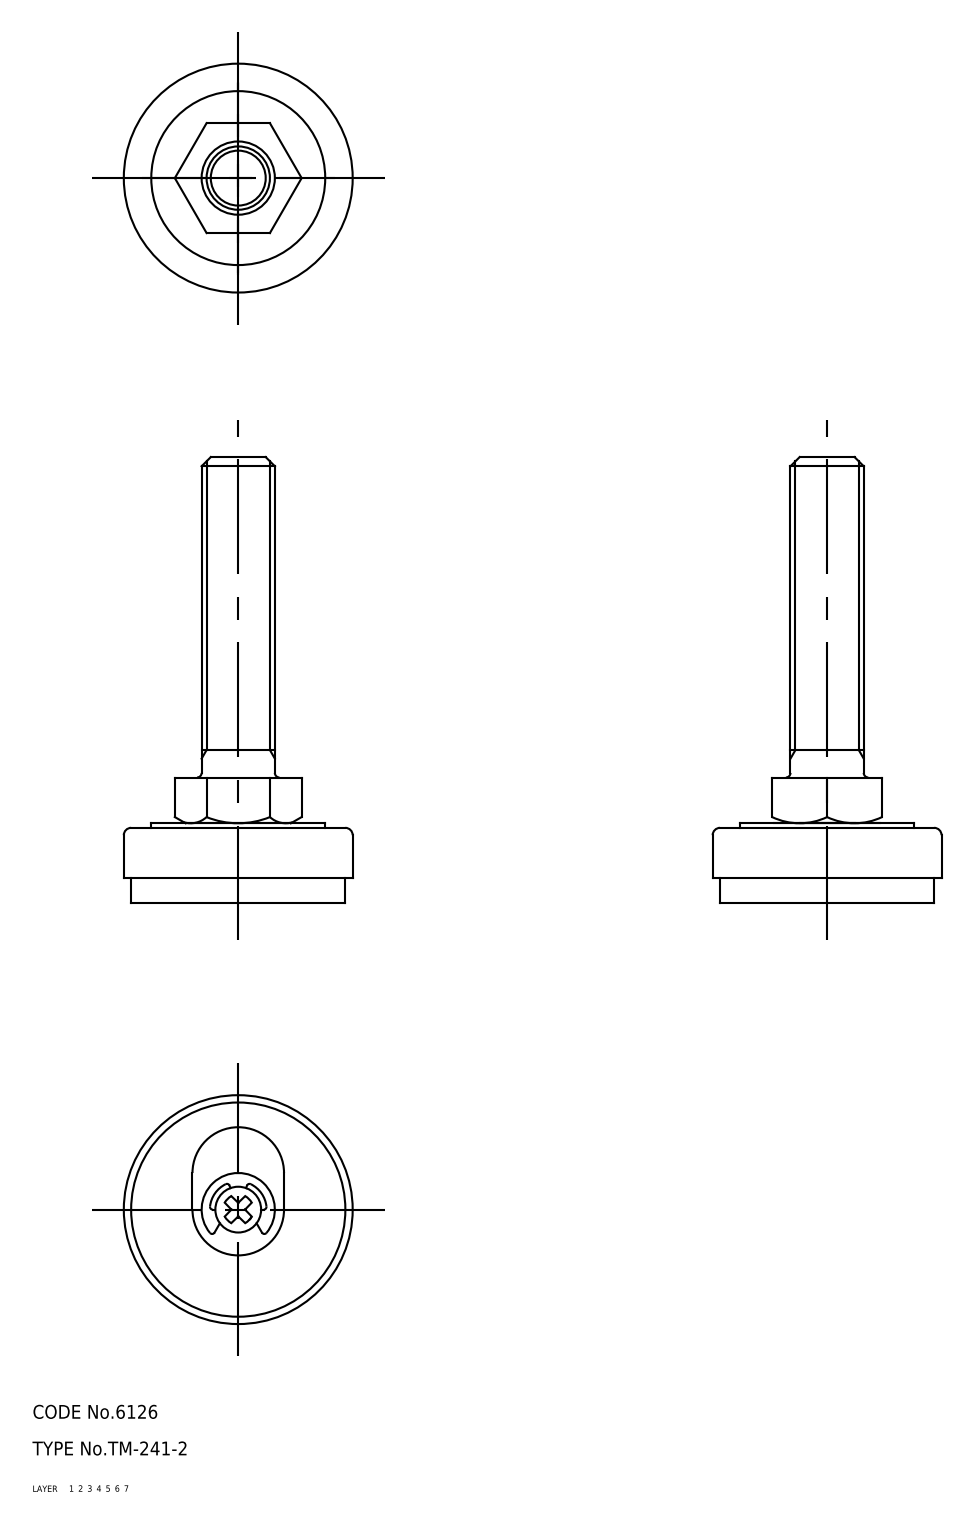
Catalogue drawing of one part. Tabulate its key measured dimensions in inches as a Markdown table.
| quantity | value |
| --- | --- |
| part name | washer; rubber pad; retainer; cover (+3 more) |
| STEP written by | CADfix (AUTOMOTIVE_DESIGN) |
| units | inches |
| bodies | 6 solids, 115 faces (0 planar, 0 cylindrical, 115 other) |
| overall size | 3.839 × 1.969 × 1.969 |
| volume | 2.938 in³ |
| surface area | 39.77 in² |
